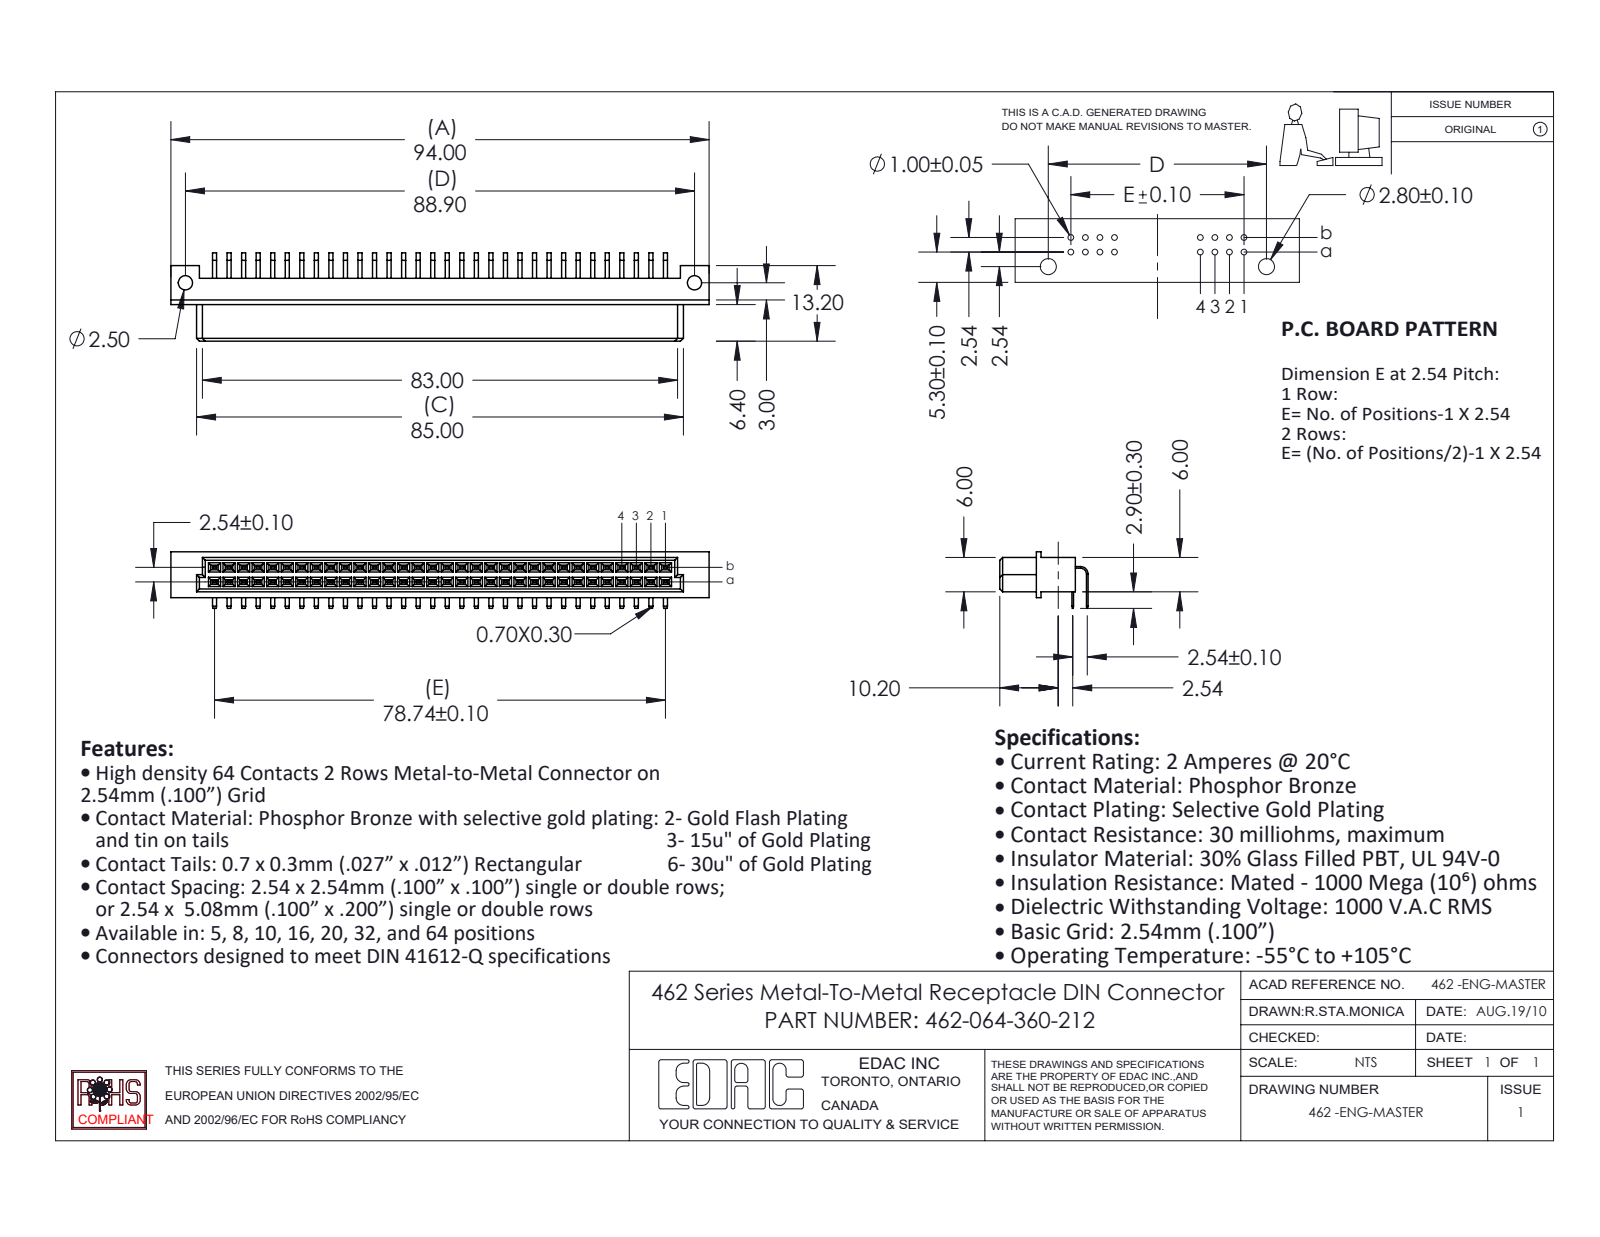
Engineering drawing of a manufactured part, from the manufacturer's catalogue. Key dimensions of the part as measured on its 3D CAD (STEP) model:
Part name (STEP PRODUCT): 462-290-1; 462-290-2; 462-064-360-212; 462 Part_64
STEP written by: SolidWorks 2020 (CONFIG_CONTROL_DESIGN)
Units: millimetres
Bodies: 65 solids, 1763 faces (1631 planar, 132 cylindrical, 0 other)
Overall size (bounding box): 94 × 15.43 × 9.9
Volume: 5 650 mm³ · Surface area: 7 447 mm²
Round holes (diameter × count): ⌀2.5 ×2
Partial cylindrical surfaces — rounded edges, fillets, slot ends (radius × count): R1.02 ×2, R1.32 ×2
Main face-to-face distances: 2.54, 6, 0.81, 0.55, 1.58, 4.42, 1.88, 4.12, 0.56, 4.6
Hole centre spacings: 88.9
